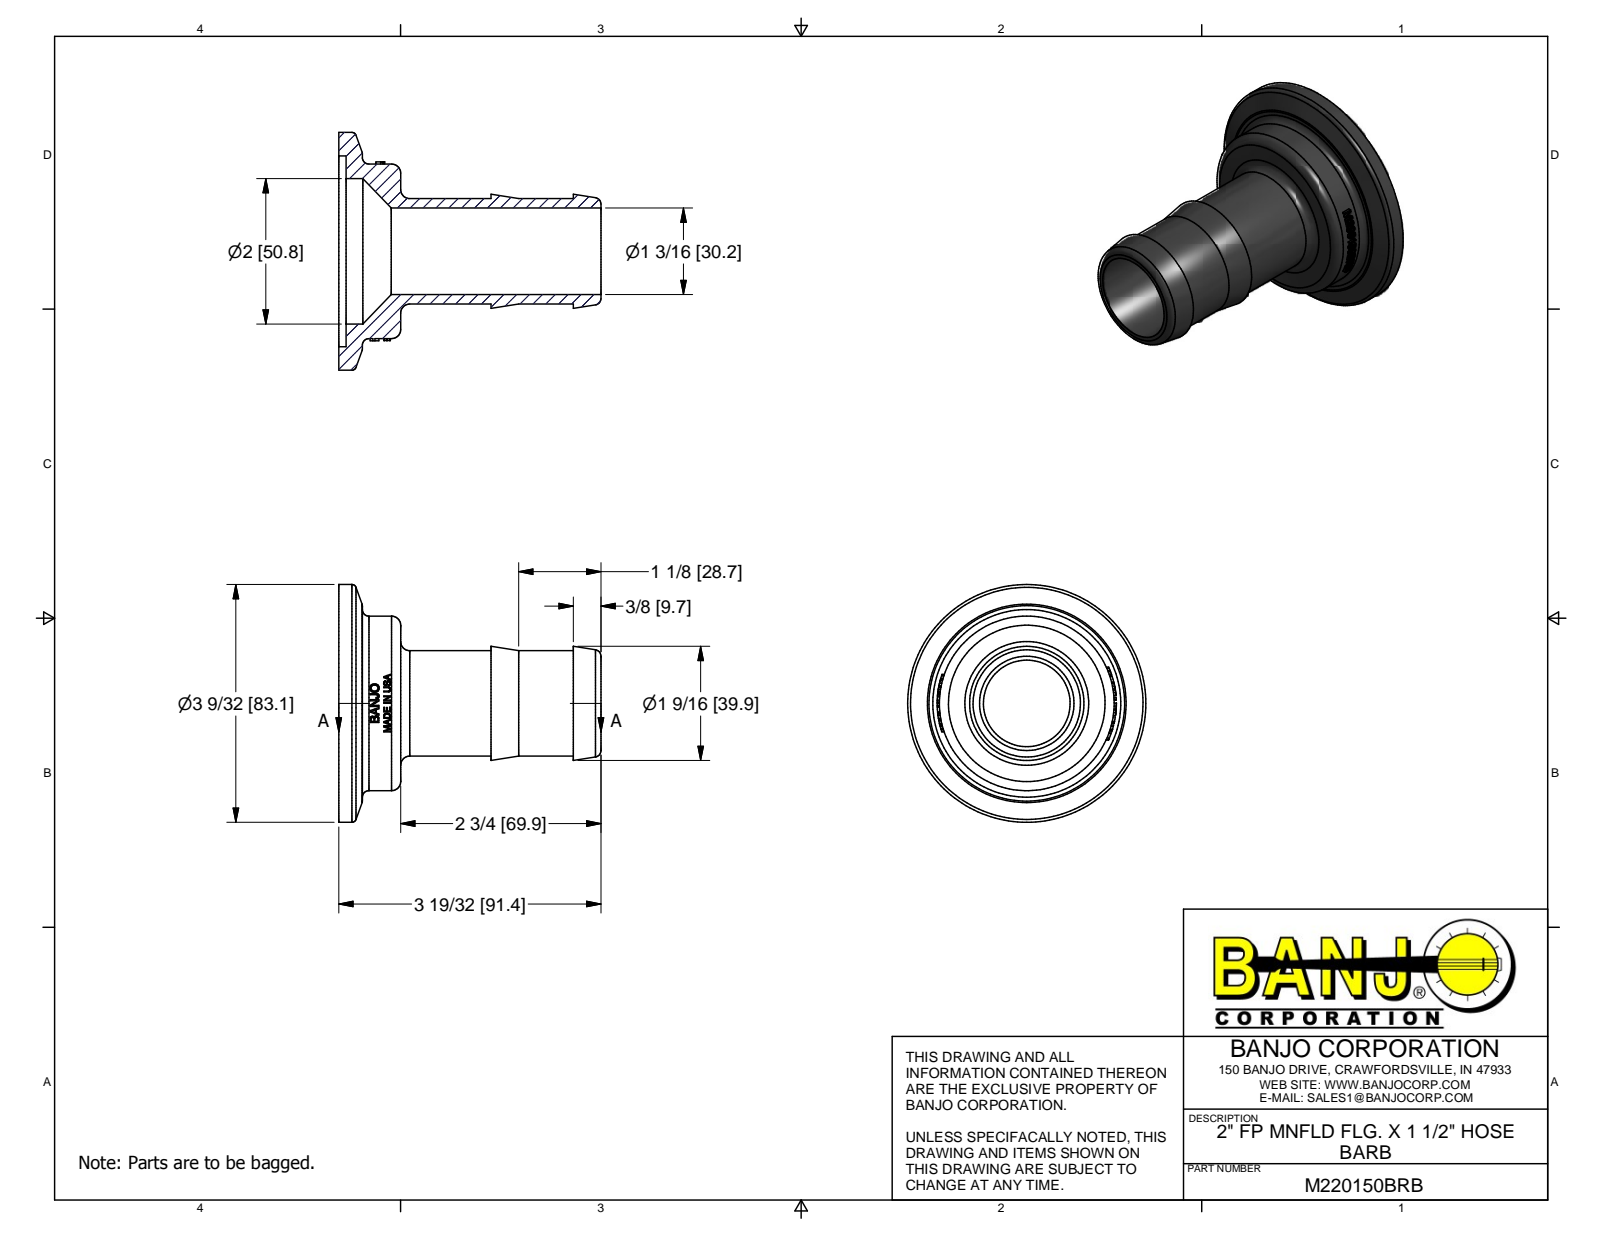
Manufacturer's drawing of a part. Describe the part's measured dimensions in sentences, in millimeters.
The part is named "M220150BRB". Its 3-D file was written by "Autodesk Inventor 2014 (AUTOMOTIVE_DESIGN)". It is 1 solid with 378 faces: 180 planar, 46 cylindrical and 152 other. Overall it measures 91.44 by 83.06 by 83.06 millimeters. Its volume is 70 613 cubic millimeters and its surface area 30 360 square millimeters. Round holes: 1 of diameter 30.23, 1 of diameter 50.8, 1 of diameter 66.67. Round bosses or shafts: 1 of diameter 83.06, 1 of diameter 60.96, 1 of diameter 36.83. Partial cylindrical surfaces (rounded edges, fillets, slot ends): 1 of radius 31.24. The main face-to-face distances are 2.54, 21.59, 19.05, 8.24, 5.7, 13.35, 91.44, 88.9, 83.2, 69.85.
